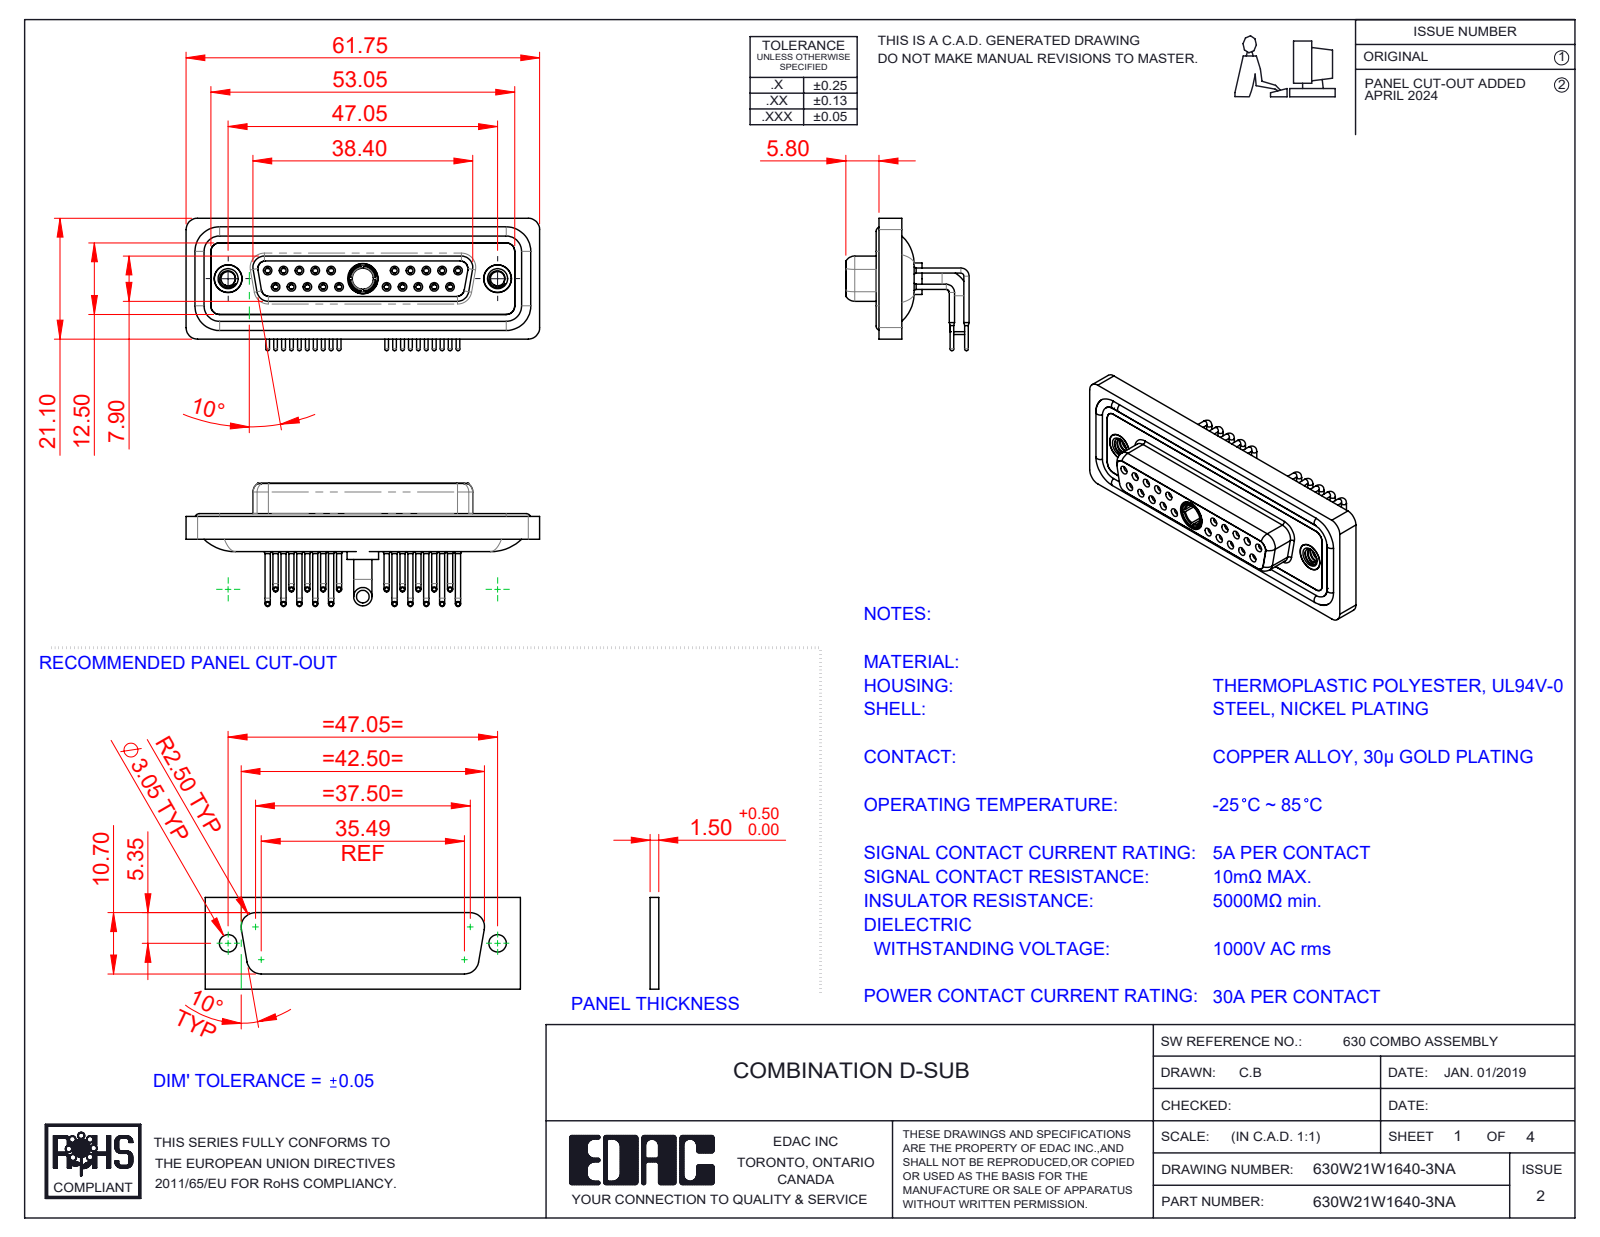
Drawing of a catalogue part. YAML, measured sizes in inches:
part_name: "630Combo Shell Rear_25 Contacts; 630Combo Contact Row 1_50 Contacts; 630Combo Shell Front_25 Contacts; 630Combo Contact Row 2_50 Contacts (+5 more)"
step_written_by: "SolidWorks 2023 (CONFIG_CONTROL_DESIGN)"
units: inches
bodies: {solids: 29, faces: 1518, planar: 434, cylindrical: 671, other: 413}
overall_size: [2.431, 0.91, 0.848]
volume: 0.52
surface_area: 22.94
round_holes:
  - {diameter: 0.035, count: 20}
  - {diameter: 0.043, count: 20}
  - {diameter: 0.059, count: 20}
  - {diameter: 0.079, count: 20}
  - {diameter: 0.063, count: 10}
  - {diameter: 0.067, count: 10}
  - {diameter: 0.191, count: 3}
  - {diameter: 0.098, count: 2}
  - {diameter: 0.157, count: 2}
  - {diameter: 0.159, count: 2}
  - {diameter: 0.197, count: 2}
  - {diameter: 0.146, count: 1}
round_bosses_or_shafts:
  - {diameter: 0.035, count: 20}
  - {diameter: 0.026, count: 20}
  - {diameter: 0.063, count: 14}
  - {diameter: 0.195, count: 2}
  - {diameter: 0.189, count: 2}
  - {diameter: 0.126, count: 2}
  - {diameter: 0.217, count: 1}
  - {diameter: 0.205, count: 1}
partial_cylinders:
  - {radius: 0.059, count: 18}
  - {radius: 0.079, count: 18}
  - {radius: 0.053, count: 8}
  - {radius: 0.063, count: 8}
  - {radius: 0.01, count: 4}
  - {radius: 0.02, count: 4}
  - {radius: 0.024, count: 4}
  - {radius: 0.026, count: 4}
face_to_face_distances: [0.016, 0.071, 0.161, 0.063, 0.043, 0.098, 0.122, 0.059, 0.386, 0.018]
hole_center_spacings: [0.124, 0.109, 0.218, 0.327, 0.198, 0.763, 0.826, 0.872]
